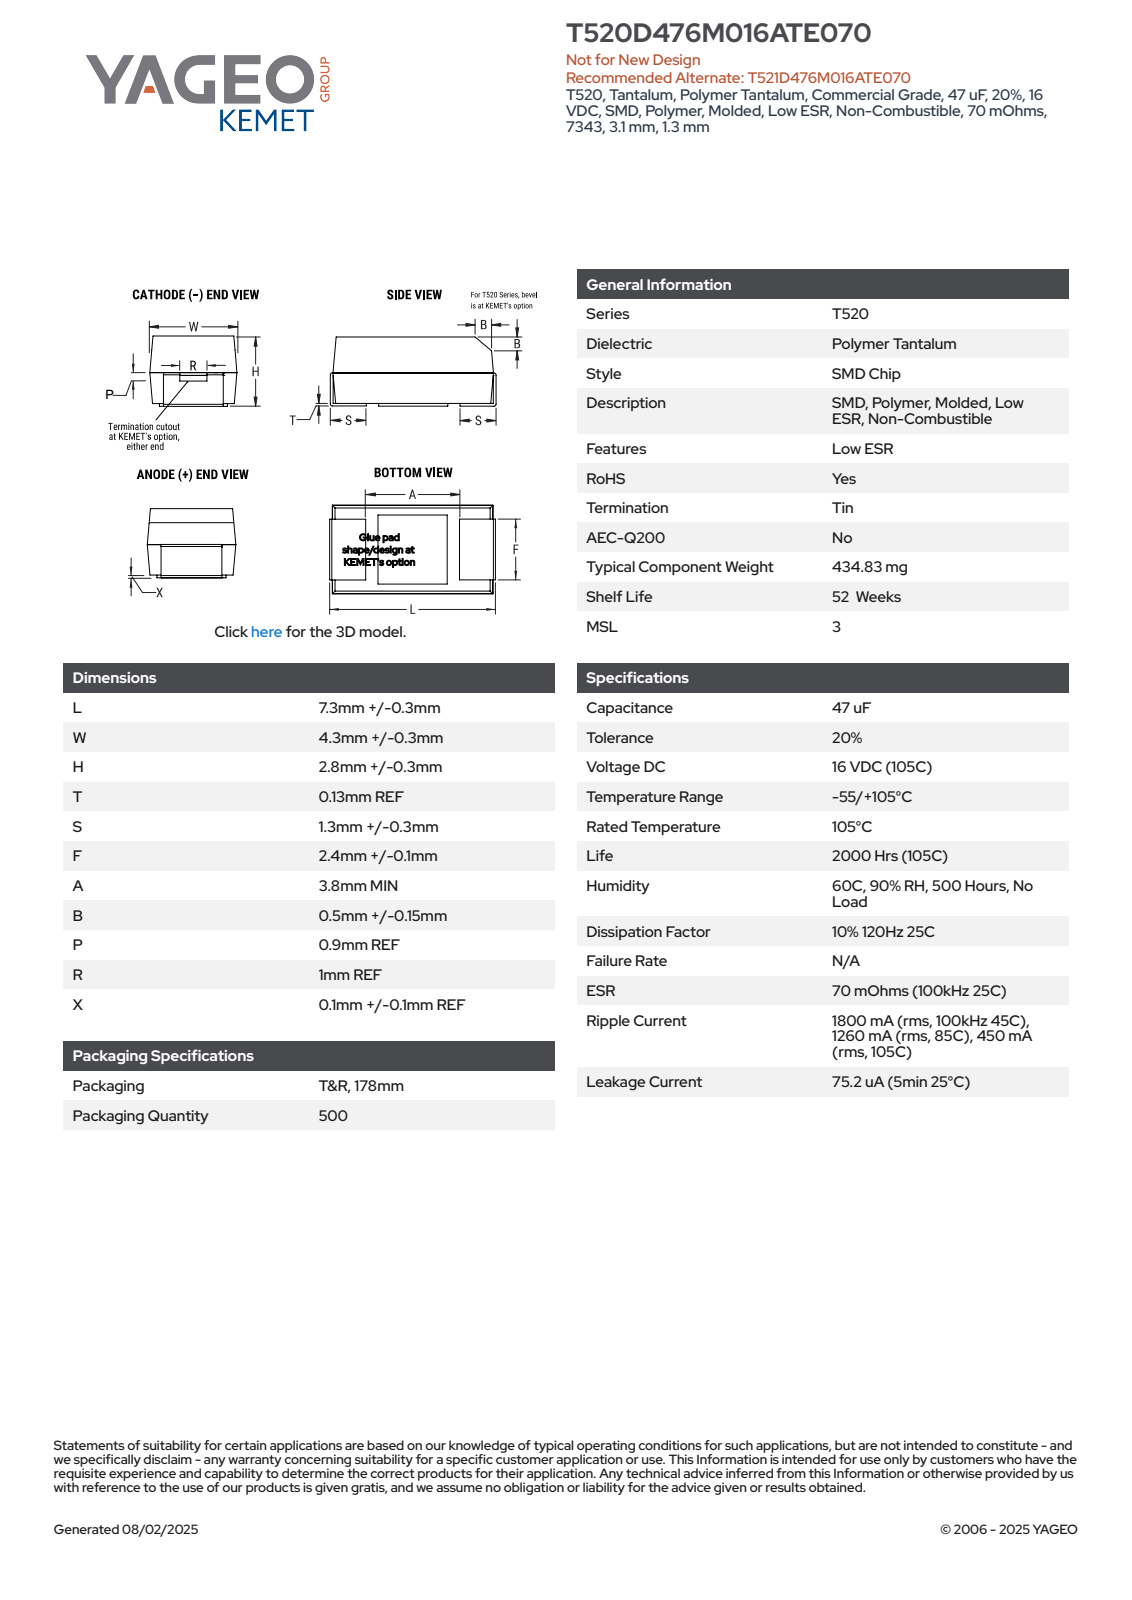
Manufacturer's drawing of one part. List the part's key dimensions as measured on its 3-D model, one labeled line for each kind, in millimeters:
Part name (STEP PRODUCT): Case_Cathode_21; Case_Bottom_21; Case_Anode_21; Case_Top_21 (+1 more)
STEP written by: SolidWorks 2014 (AUTOMOTIVE_DESIGN)
Units: millimetres
Bodies: 7 solids, 100 faces (95 planar, 5 cylindrical, 0 other)
Overall size (bounding box): 7.6 × 4.6 × 3.1
Volume: 98 mm³ · Surface area: 228 mm²
Main face-to-face distances: 1.57, 1.4, 2.97, 4.58, 1.5, 3.07, 7.31, 1.53, 3.1, 7.47
